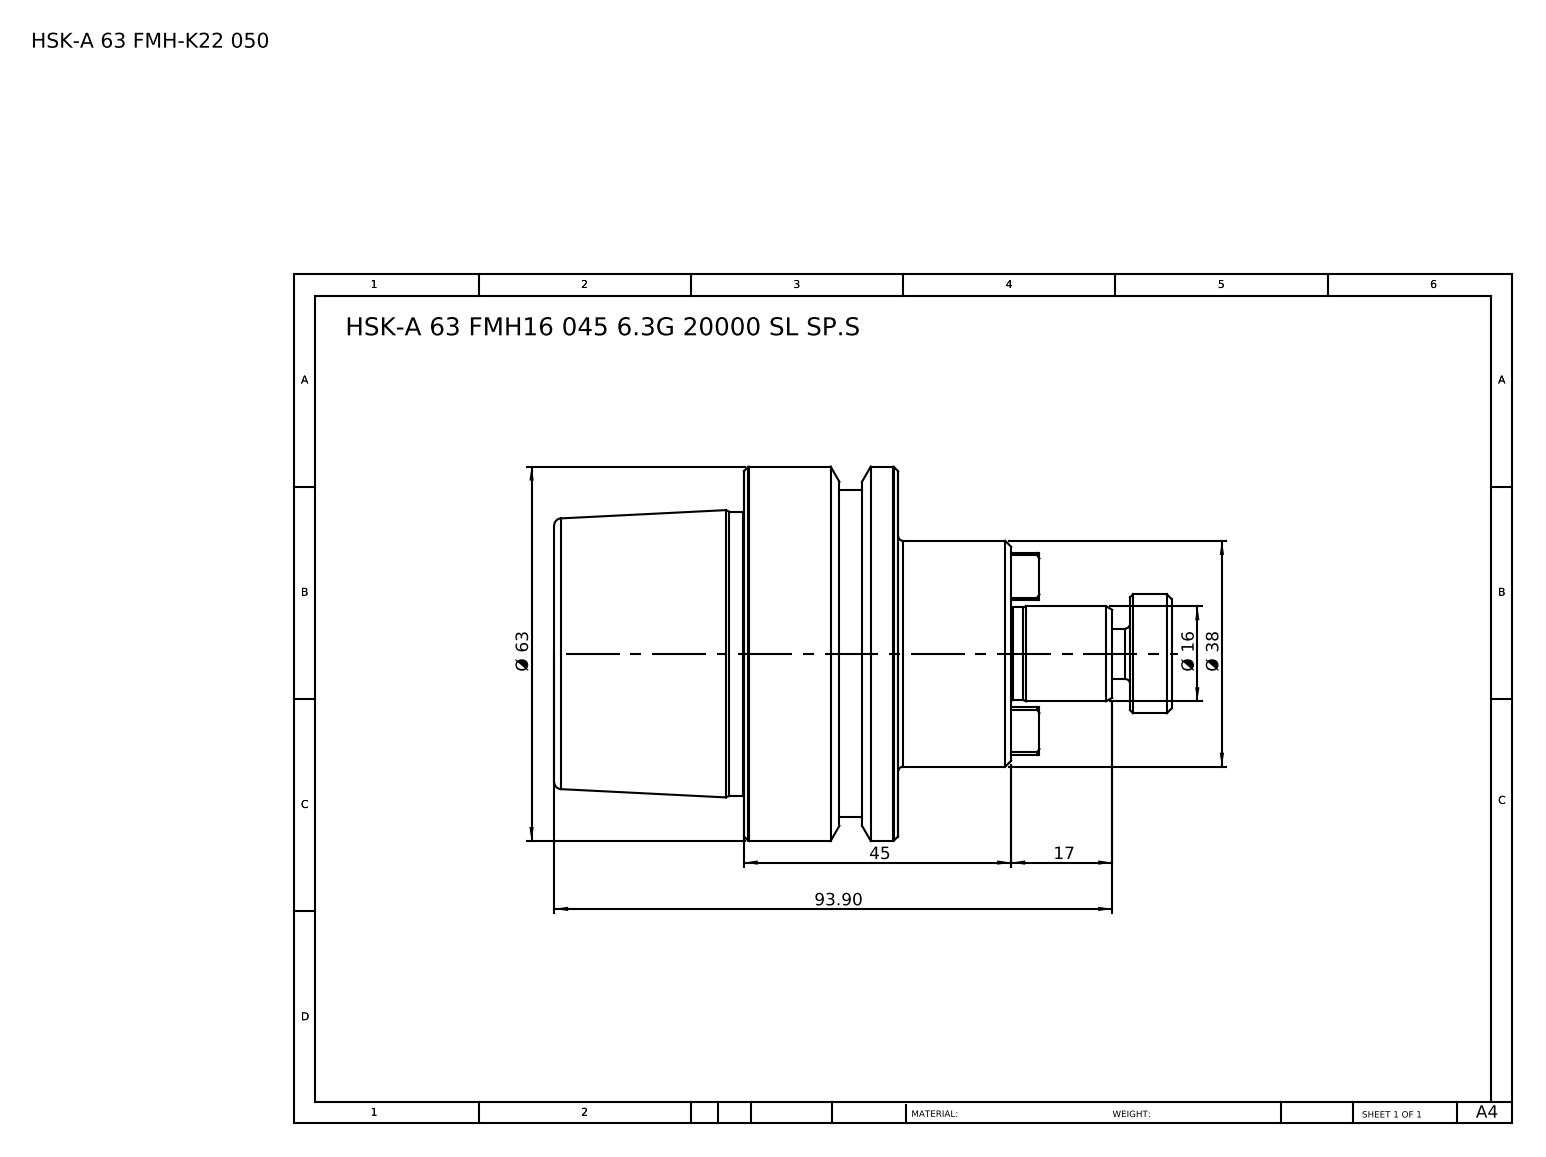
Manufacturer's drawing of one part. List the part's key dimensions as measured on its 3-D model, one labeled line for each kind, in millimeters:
Part name (STEP PRODUCT): HSK-A 63 FMH-K16 045 6.3G 20000 SL SP
STEP written by: SolidWorks 2014 (CONFIG_CONTROL_DESIGN)
Units: millimetres
Bodies: 1 solid, 99 faces (37 planar, 18 cylindrical, 44 other)
Overall size (bounding box): 103.9 × 63 × 63
Volume: 160 399 mm³ · Surface area: 20 922 mm²
Round bosses / shafts (diameter × count): ⌀63 ×1, ⌀55 ×1, ⌀47.78 ×1, ⌀38 ×1, ⌀20 ×1, ⌀16 ×1, ⌀15.6 ×1, ⌀8.5 ×1
Main face-to-face distances: 57.9, 26, 31.9, 19, 45, 76.9, 27, 46, 72, 103.9
